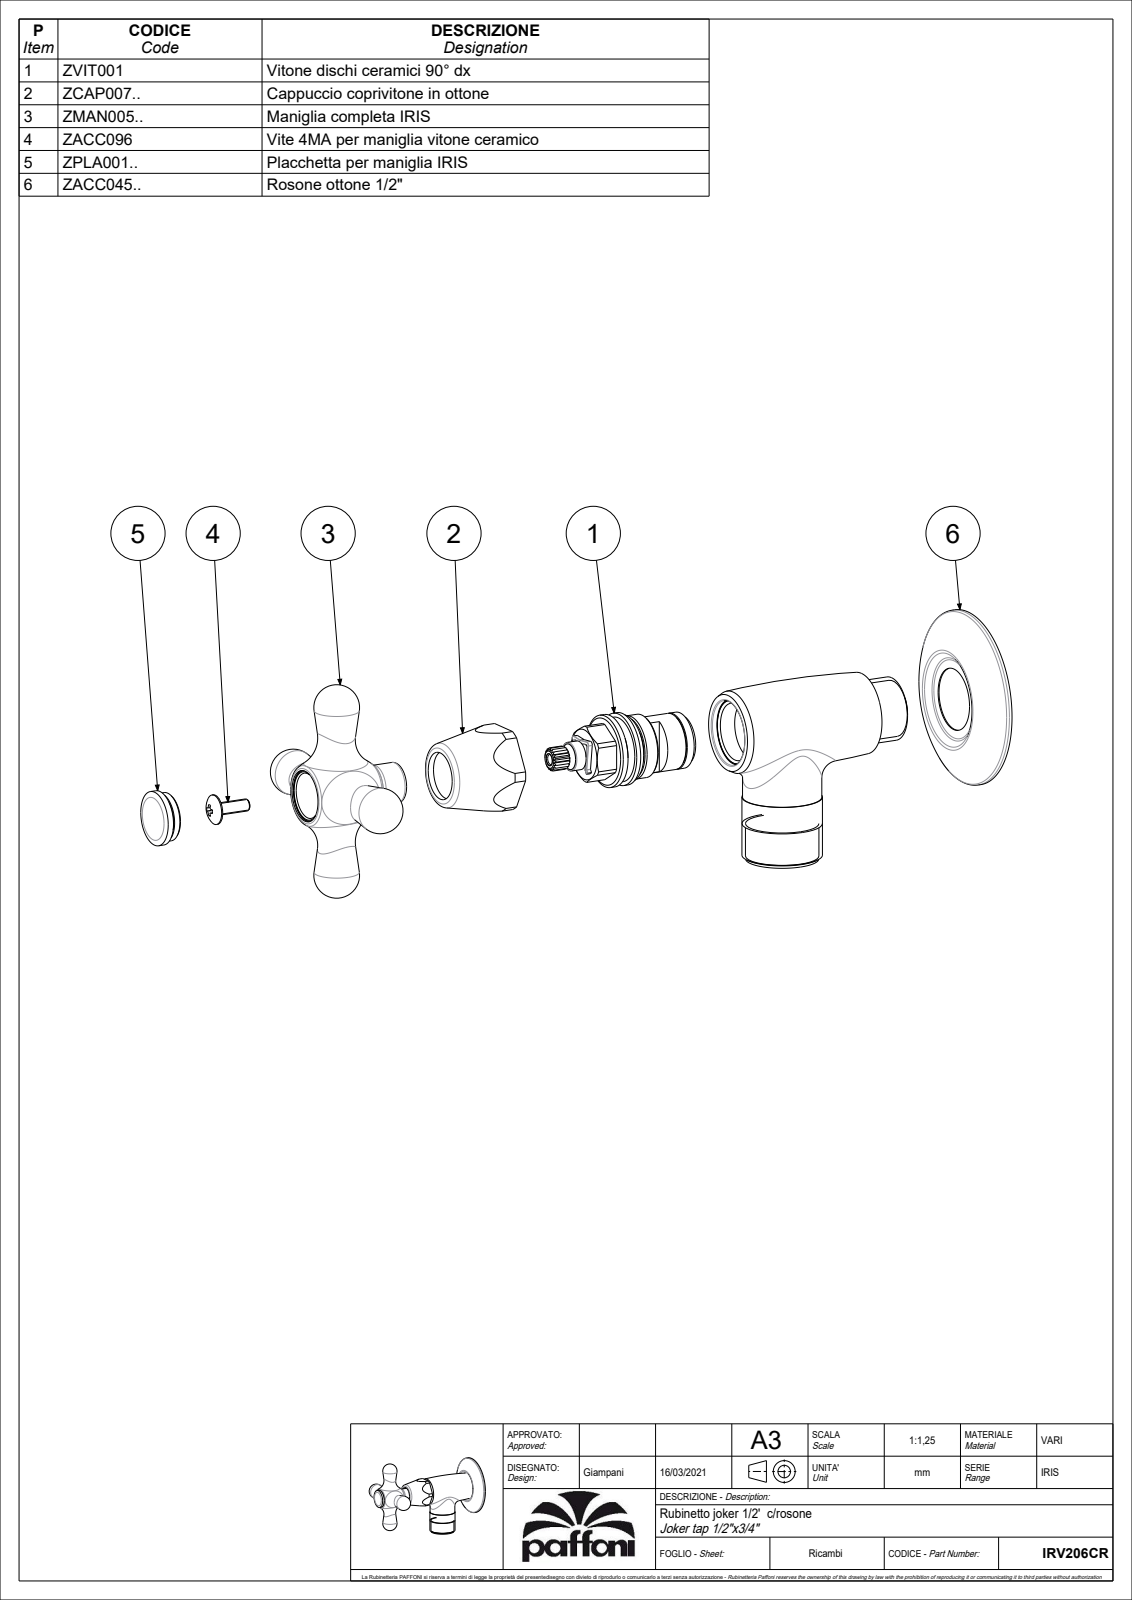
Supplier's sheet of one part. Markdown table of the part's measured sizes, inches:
| quantity | value |
| --- | --- |
| part name | IRV206CR |
| STEP written by | CREO PARAMETRIC BY PTC INC, 2020044 (CONFIG_CONTROL_DESIGN) |
| units | inches |
| bodies | 1 solid, 100 faces (14 planar, 20 cylindrical, 66 other) |
| overall size | 4.772 × 3.209 × 2.835 |
| volume | 6.277 in³ |
| surface area | 33.19 in² |
| round bosses / shafts (diameter × count) | 2.283 × 1, 1.039 × 1, 1.024 × 1, 0.945 × 1, 0.827 × 1, 0.709 × 1, 0.531 × 1 |
| partial cylindrical surfaces (radius × count) | 0.571 × 1 |
| main face-to-face distances | 1.043, 0.264, 3.406, 3.142, 1.27, 2.313, 2.461, 2.197, 0.945, 0.039 |
